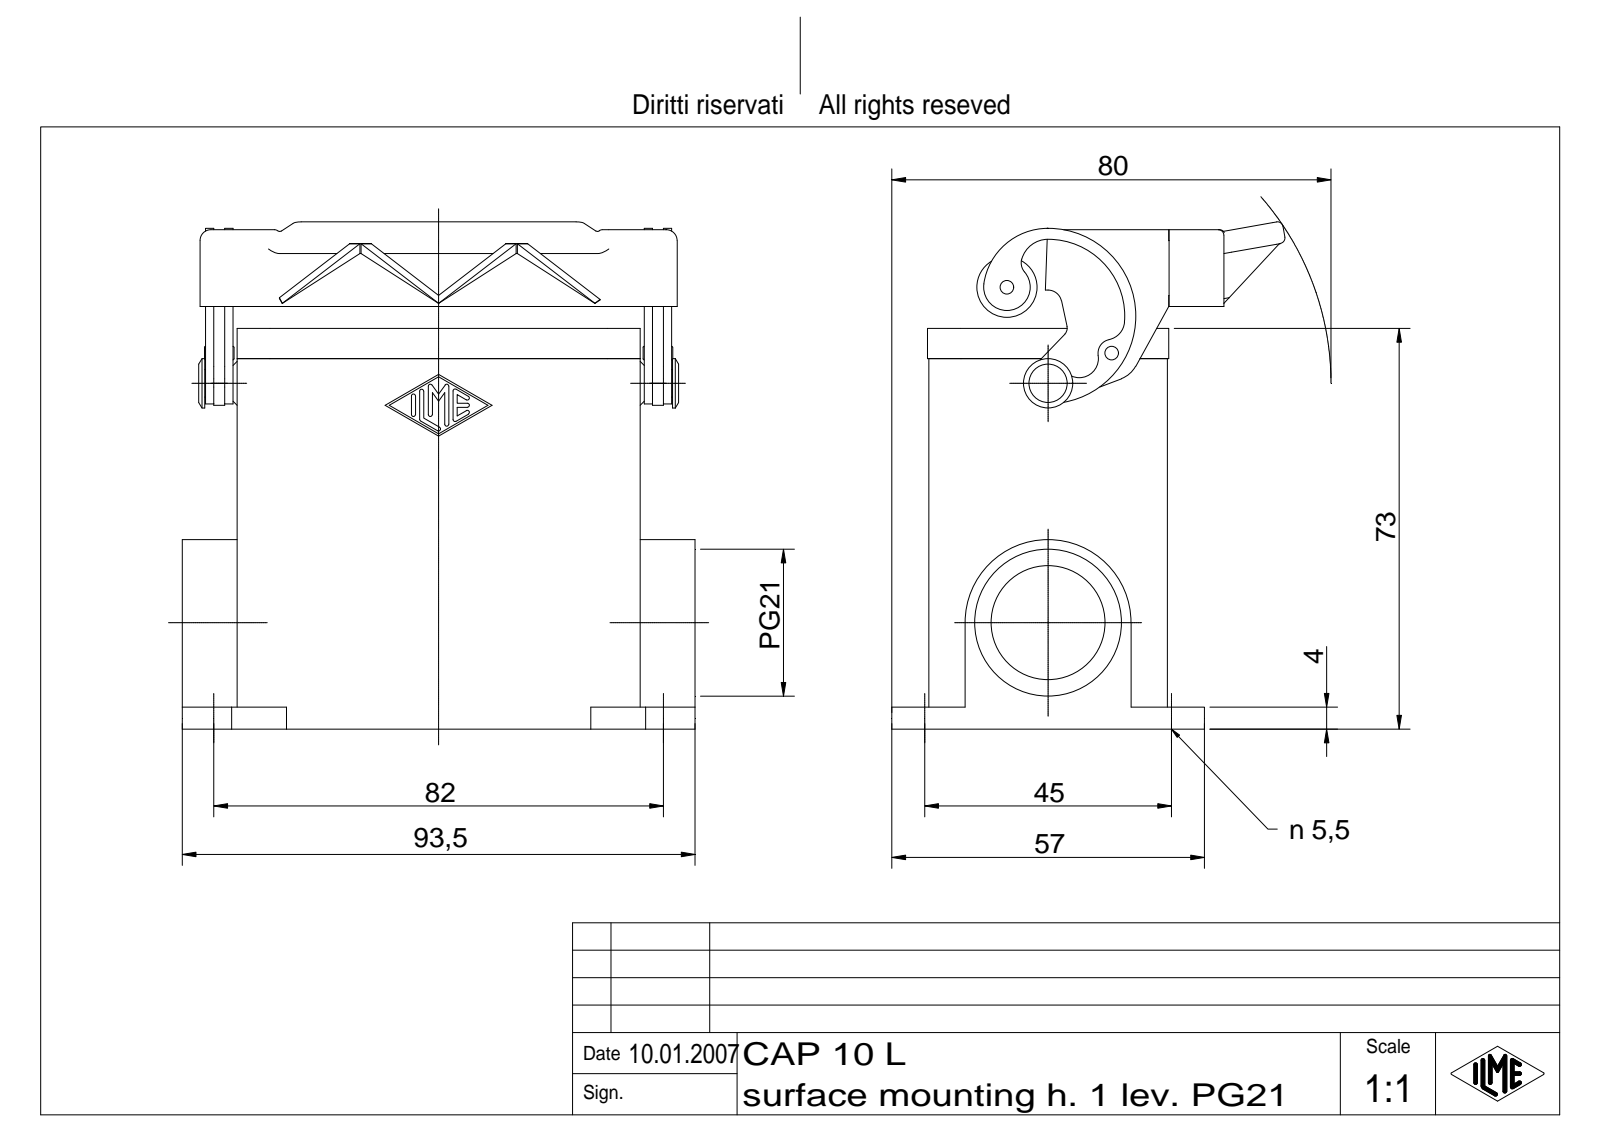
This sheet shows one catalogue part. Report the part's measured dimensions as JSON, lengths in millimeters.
{"part_name": "CAP 10 L", "step_written_by": "Autodesk Inventor 7 (AUTOMOTIVE_DESIGN)", "units": "millimeters", "bodies": {"solids": 4, "faces": 432, "planar": 164, "cylindrical": 123, "other": 145}, "overall_size": [93.5, 92.42, 71.7], "volume_mm3": 103913, "surface_area_mm2": 54169, "round_holes": [[5.5, 4], [2, 1], [20.78, 1], [26.78, 1]], "round_bosses_or_shafts": [[11, 1], [9, 1], [5, 1], [3, 1], [2.5, 1]], "partial_cylinders_radius": [[0.38, 14], [2, 12], [6, 8], [1, 7], [1.5, 5], [3, 4], [2.5, 3], [3.5, 2]], "face_to_face_distances": [3, 40.5, 4, 43.5, 37.5, 11.75, 67.5, 61.75, 8.75, 63.5], "hole_center_spacings": [45, 82, 93.54, 50.46]}
